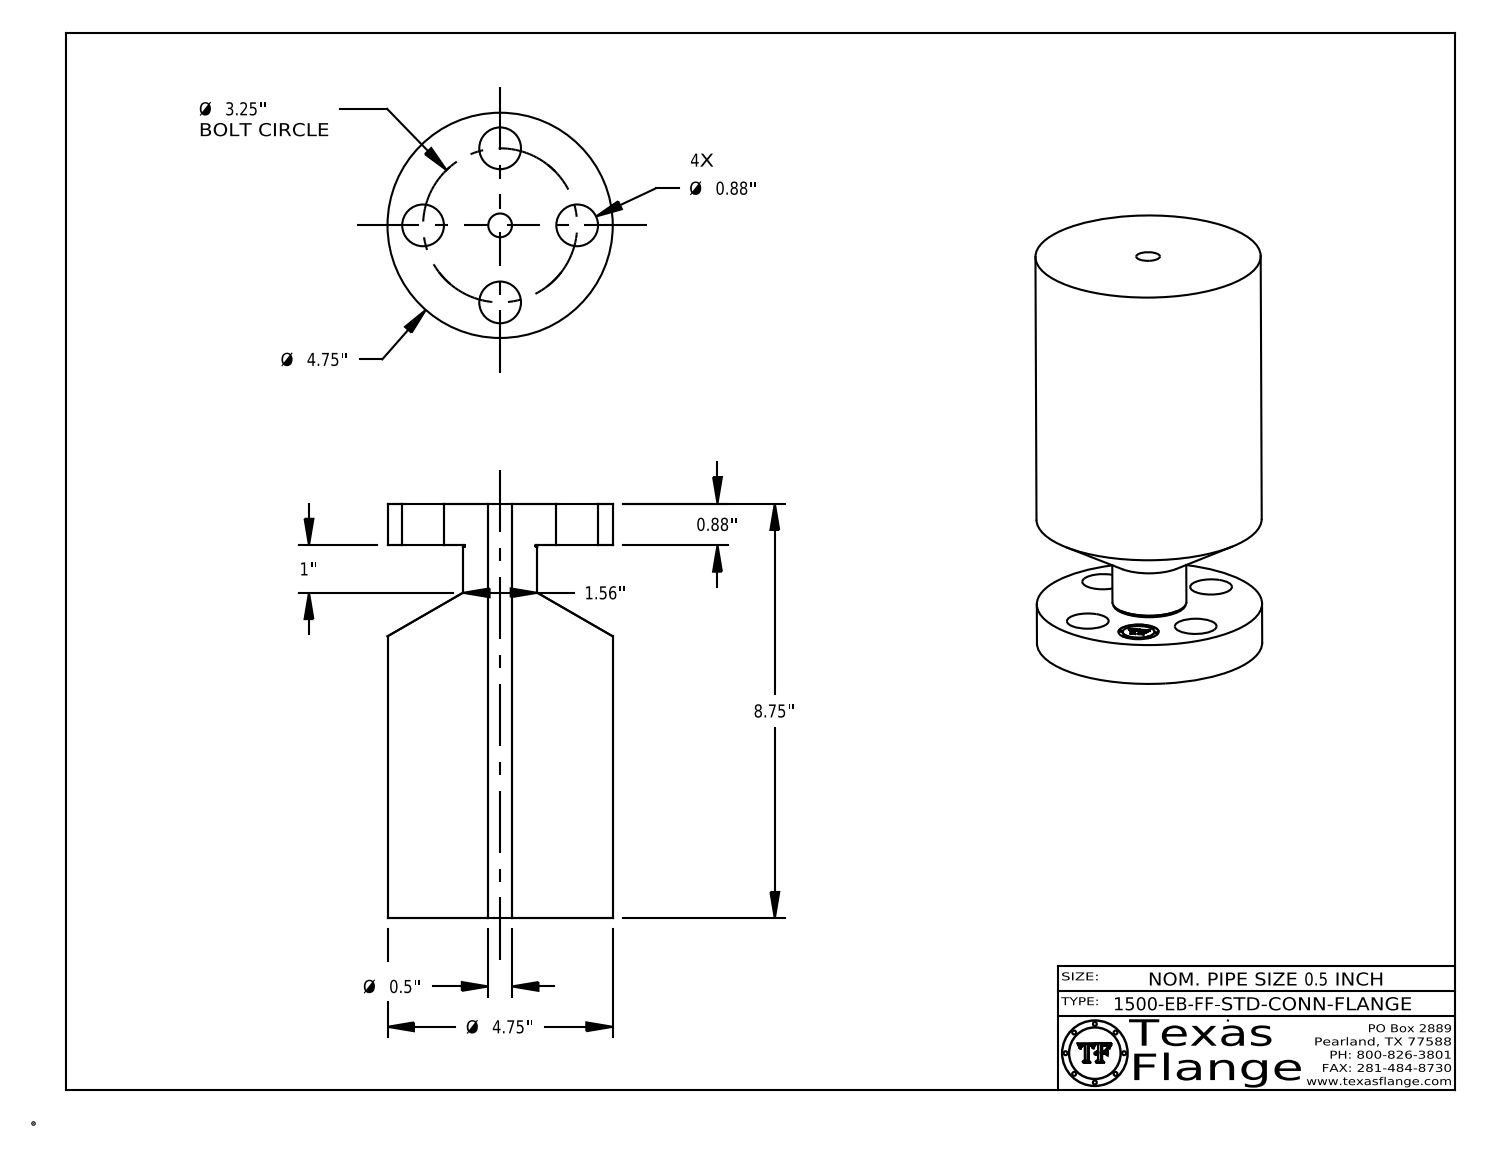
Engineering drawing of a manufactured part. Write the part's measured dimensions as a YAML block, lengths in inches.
part_name: "0.5-1500-EB-FF-STD-CONN-FLANGE"
step_written_by: "CATIA V5 STEP AP214 (AUTOMOTIVE_DESIGN)"
units: inches
bodies: {solids: 1, faces: 410, planar: 368, cylindrical: 36, other: 6}
overall_size: [8.75, 4.75, 4.75]
volume: 126.9
surface_area: 194.8
round_holes:
  - {diameter: 0.88, count: 4}
  - {diameter: 0.5, count: 1}
  - {diameter: 0.85, count: 1}
round_bosses_or_shafts:
  - {diameter: 0.051, count: 8}
  - {diameter: 4.75, count: 1}
  - {diameter: 1.56, count: 1}
  - {diameter: 0.67, count: 1}
face_to_face_distances: [8.75, 0.88, 7.87, 0.875, 7.875, 0.254, 0.248, 0.016, 0.046, 0.165]
hole_center_spacings: [1.625, 2.298, 1.244, 3.003, 3.25]
